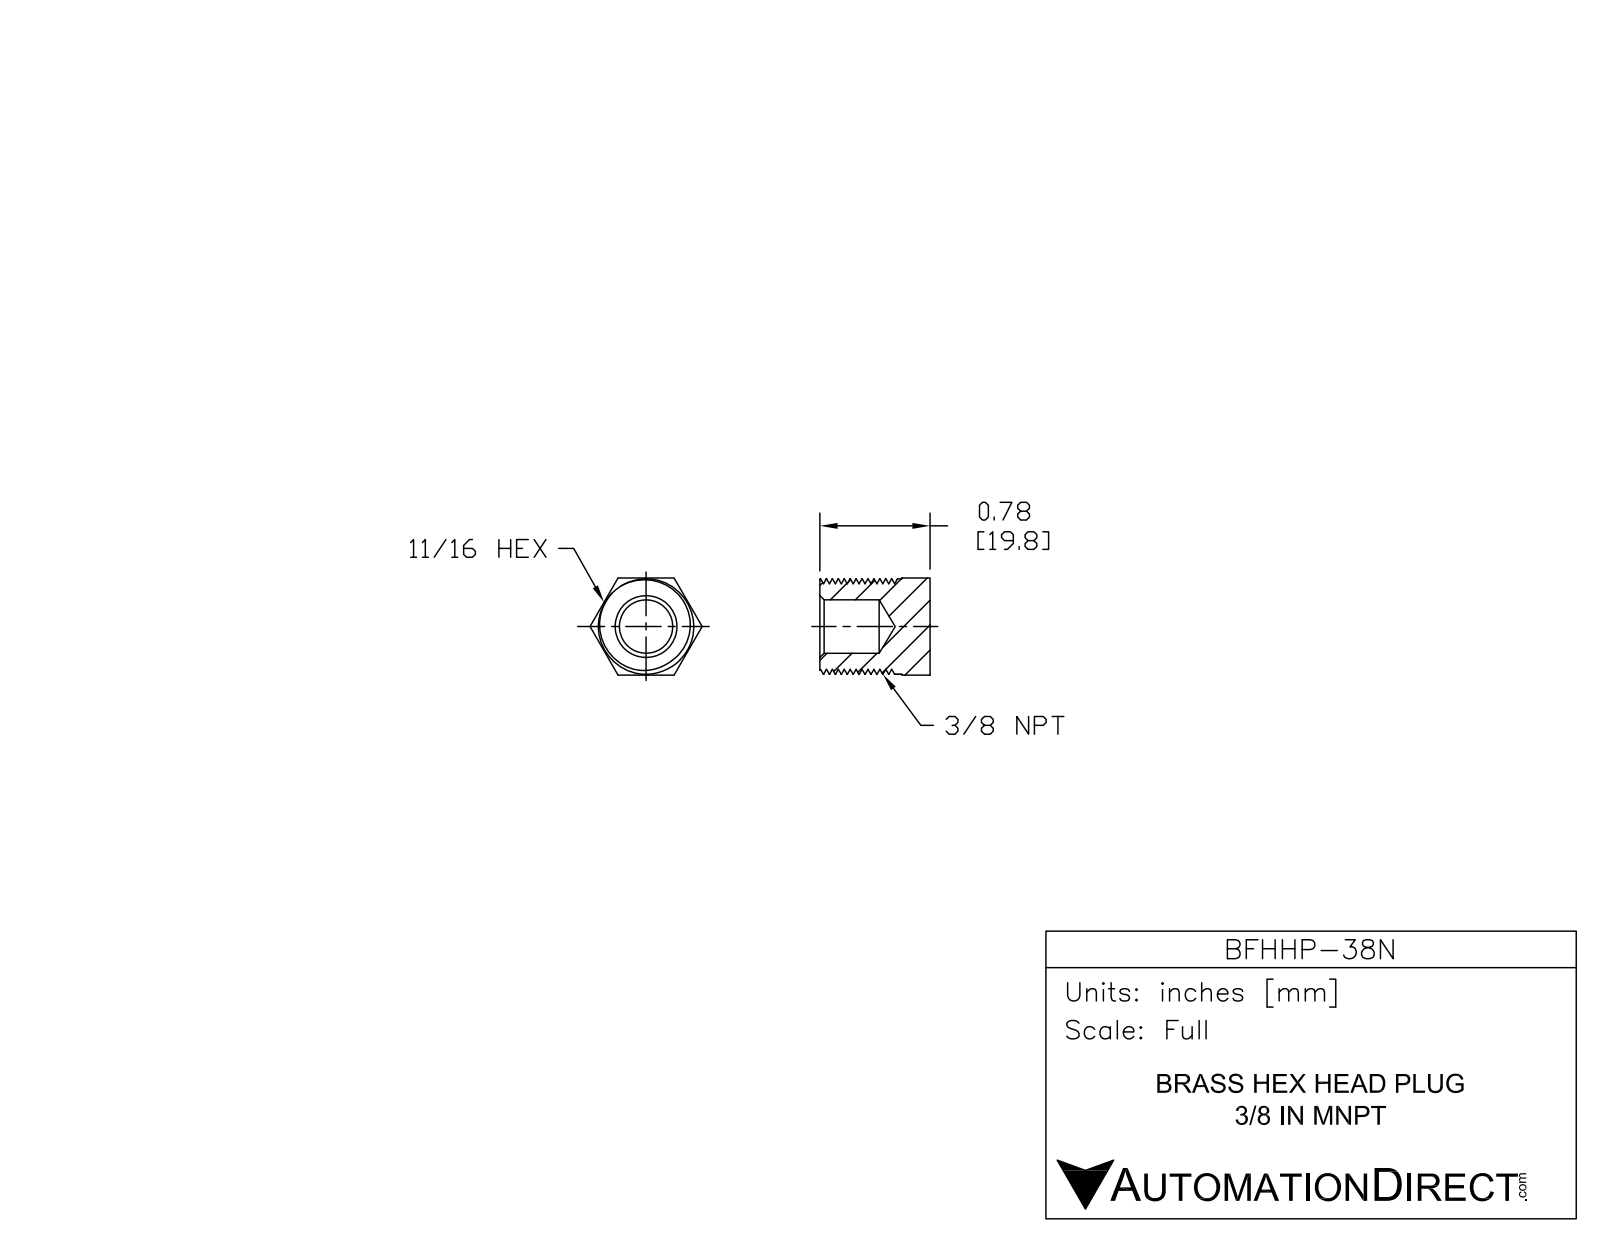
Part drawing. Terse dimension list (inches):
name: BFHHP-38N
written by: SolidWorks 2015 (CONFIG_CONTROL_DESIGN)
unit: in
bodies: 1 solid, 45 faces (10 planar, 29 cylindrical, 6 other)
size: 0.794 × 0.78 × 0.688
volume: 0.219 in³; area: 3.986 in²
holes: 1× ⌀0.378
bosses: 1× ⌀0.675
face distances: 0.688, 0.78, 0.2, 0.58
